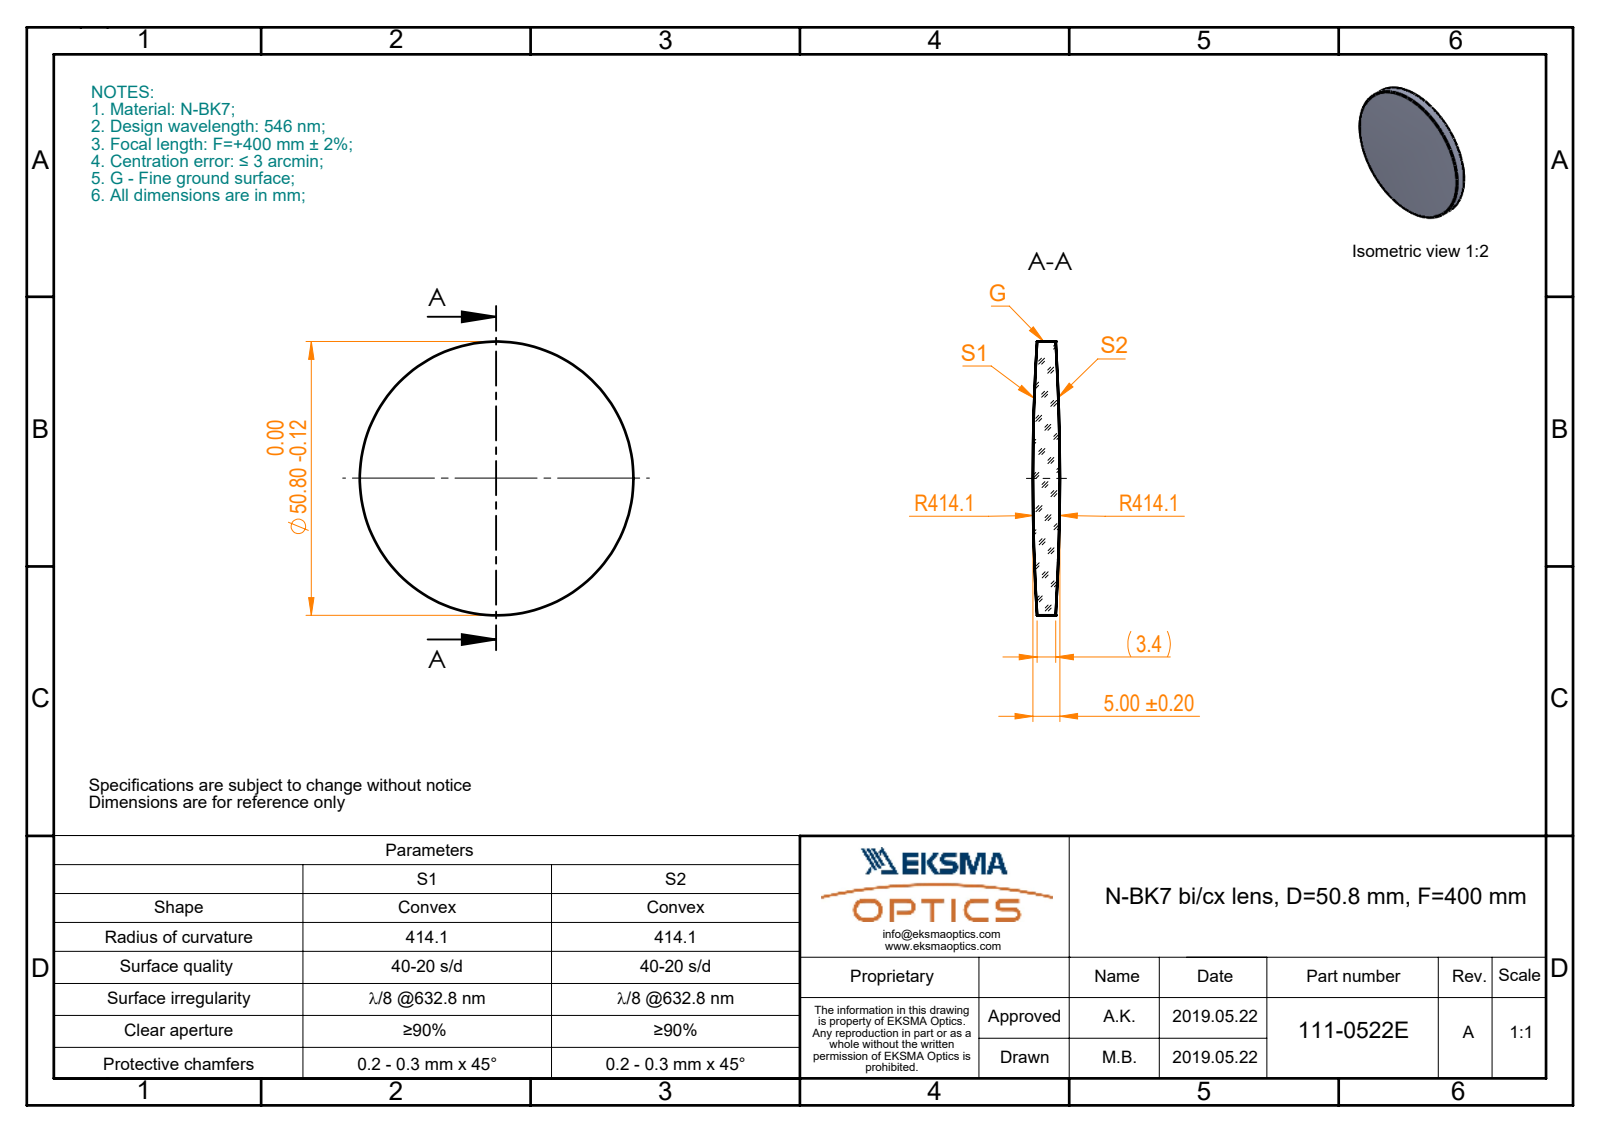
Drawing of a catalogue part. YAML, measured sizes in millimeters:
part_name: "111-0522E BK7 bi-cx 50.8 F400"
step_written_by: "SolidWorks 2017 (CONFIG_CONTROL_DESIGN)"
units: millimeters
bodies: {solids: 1, faces: 6, planar: 0, cylindrical: 2, other: 4}
overall_size: [50.8, 50.8, 5]
volume: 8554
surface_area: 4607
round_bosses_or_shafts:
  - {diameter: 50.8, count: 1}
